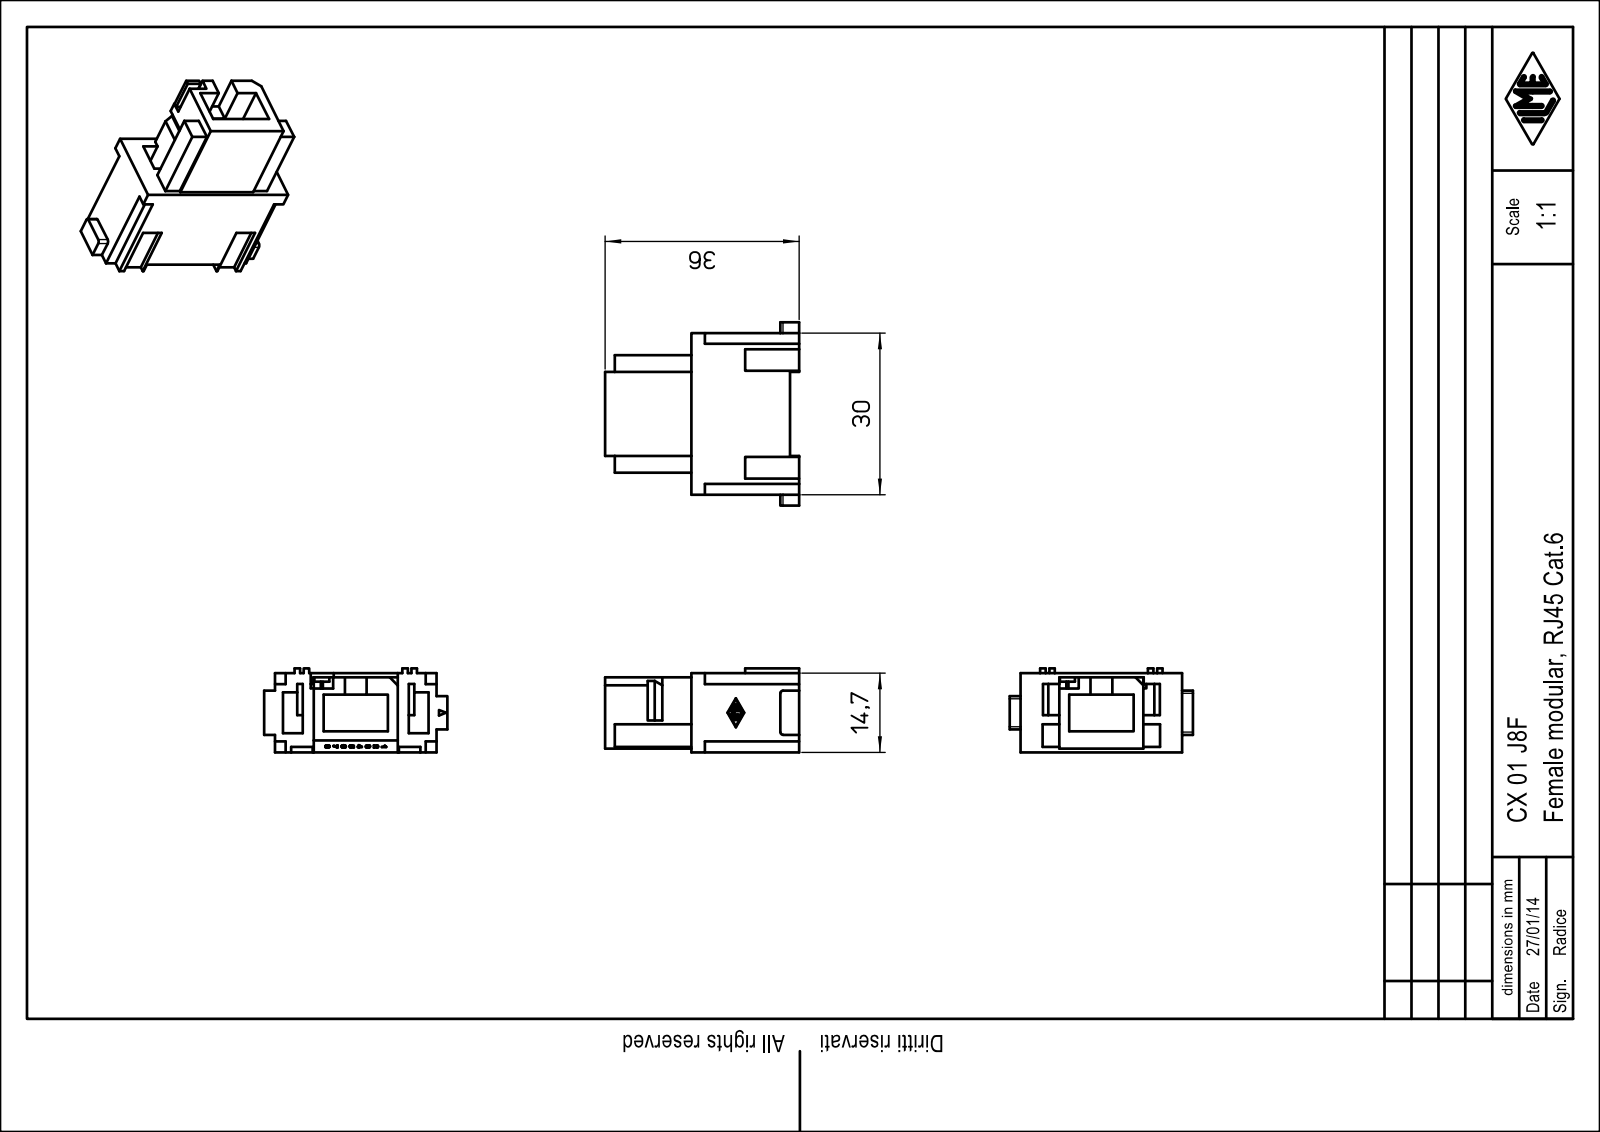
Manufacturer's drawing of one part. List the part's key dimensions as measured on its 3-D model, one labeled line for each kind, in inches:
Part name (STEP PRODUCT): CX_01_J8F
STEP written by: Creo Elements/Direct Modeling 18.0B 02-Dec-2011 (C) Parametric Technology GmbH (AUTOMOTIVE_DESIGN)
Units: inches
Bodies: 1 solid, 540 faces (522 planar, 9 cylindrical, 9 other)
Overall size (bounding box): 1.417 × 1.339 × 0.614
Volume: 0.462 in³ · Surface area: 10.03 in²
Partial cylindrical surfaces — rounded edges, fillets, slot ends (radius × count): R0.004 ×5, R0.02 ×4
Main face-to-face distances: 0.394, 0.126, 0.059, 0.579, 0.898, 0.283, 0.081, 0.154, 0.424, 0.031
